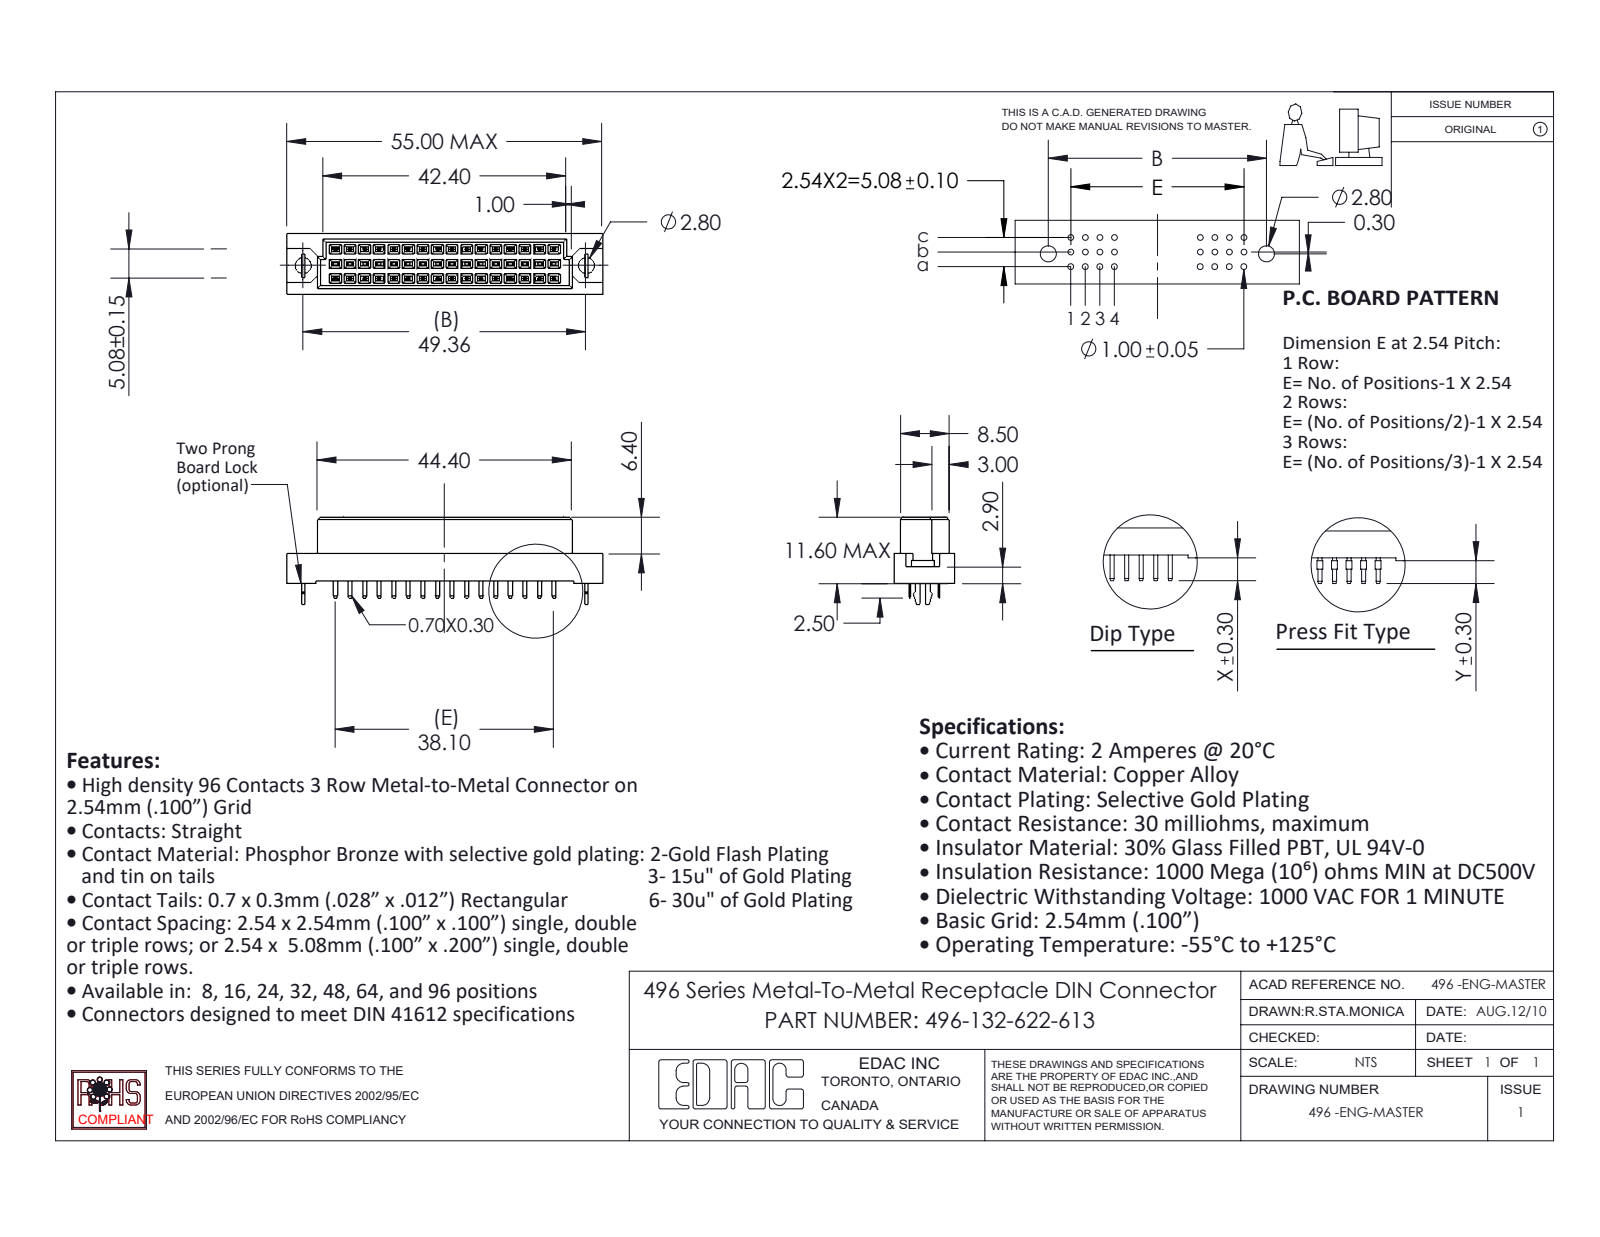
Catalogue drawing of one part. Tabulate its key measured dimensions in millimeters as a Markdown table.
| quantity | value |
| --- | --- |
| part name | 496-132-622-613; 496 Bore-lock; 496 Part_48; 496-290_22 |
| STEP written by | SolidWorks 2020 (CONFIG_CONTROL_DESIGN) |
| units | millimeters |
| bodies | 35 solids, 1022 faces (1016 planar, 6 cylindrical, 0 other) |
| overall size | 55 × 15.2 × 10.6 |
| volume | 4 657 mm³ |
| surface area | 4 766 mm² |
| round holes (diameter × count) | 2.8 × 2 |
| partial cylindrical surfaces (radius × count) | 0.53 × 1 |
| main face-to-face distances | 2.54, 5.08, 1.05, 9.55, 0.81, 0.56, 0.55, 10.6, 3.35, 1.73 |
| hole center spacings | 49.36 |
